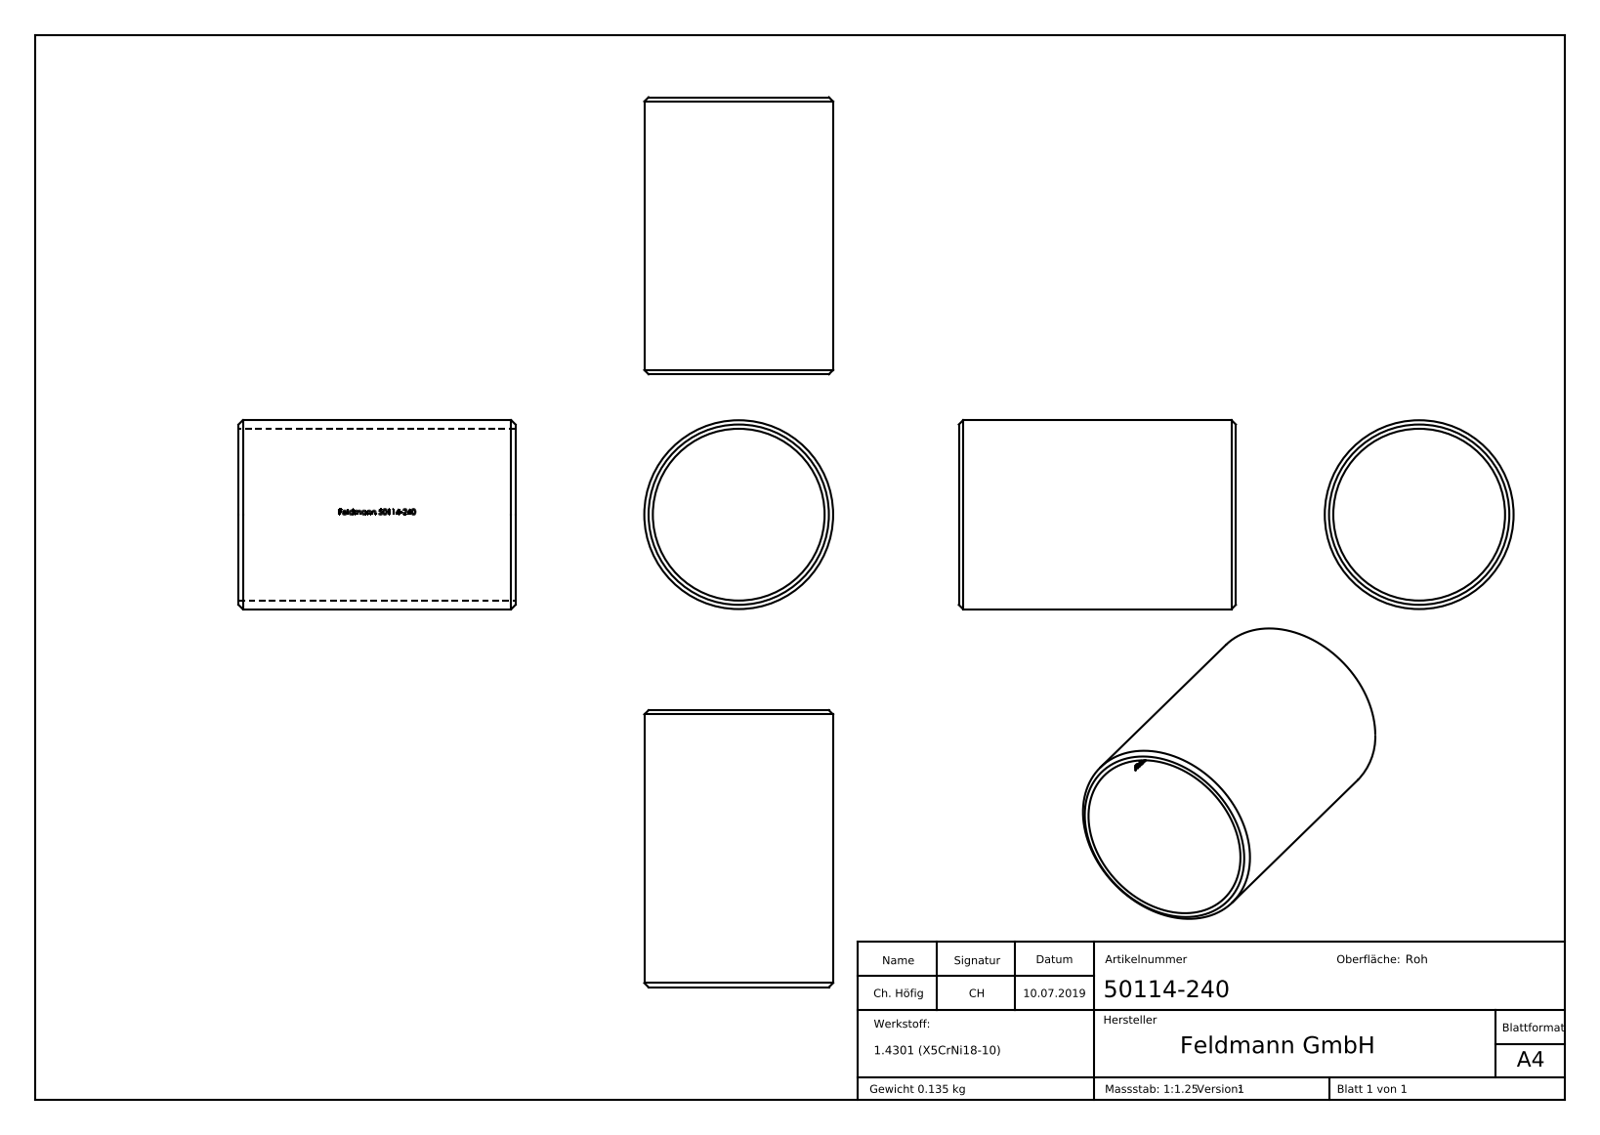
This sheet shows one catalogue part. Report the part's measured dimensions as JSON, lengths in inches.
{"part_name": "50114-240", "step_written_by": "SolidWorks 2015 (CONFIG_CONTROL_DESIGN)", "units": "inches", "bodies": {"solids": 1, "faces": 234, "planar": 110, "cylindrical": 40, "other": 84}, "overall_size": [2.559, 1.744, 1.744], "volume_in3": 1.046, "surface_area_in2": 27.36, "round_holes": [[1.587, 1]], "round_bosses_or_shafts": [[1.744, 1]], "partial_cylinders_radius": [[0.797, 1]], "face_to_face_distances": [2.559, 0.035, 0.246, 0.04, 0.017, 0.502, 0.462, 0.576, 0.049, 0.089]}
